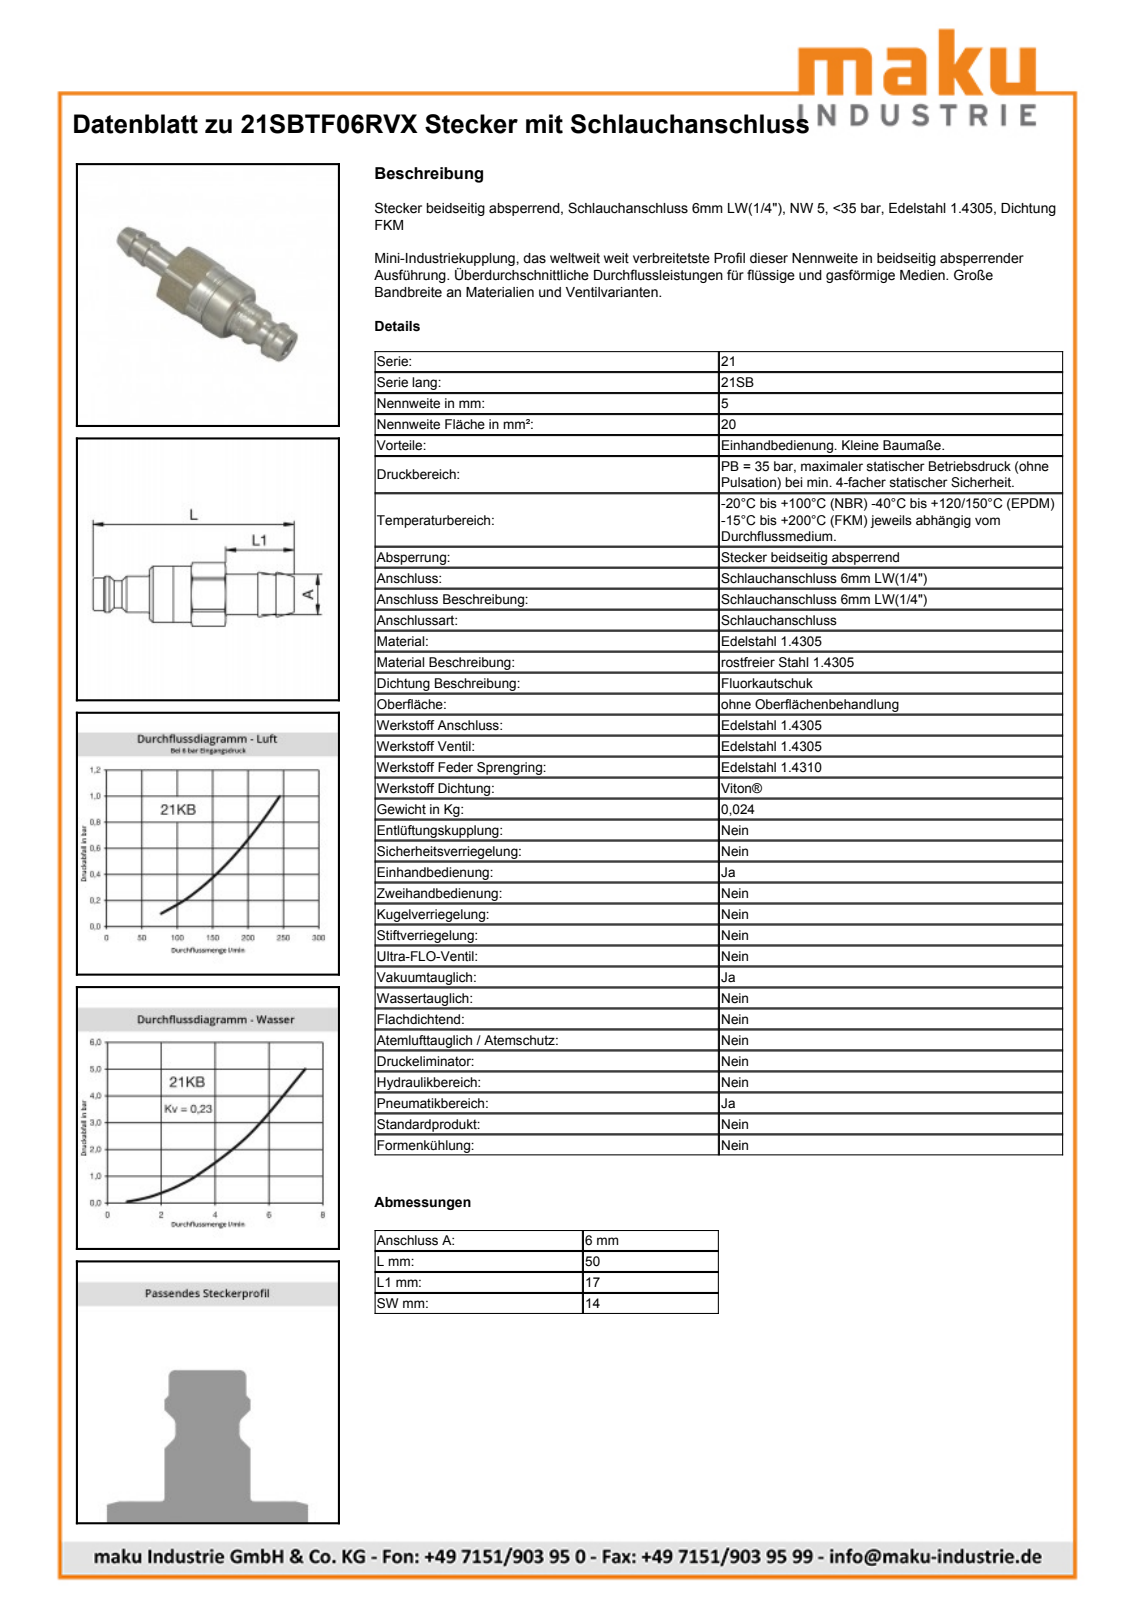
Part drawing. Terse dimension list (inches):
name: D105879
written by: Autodesk Inventor 2013 (AUTOMOTIVE_DESIGN)
unit: in
bodies: 1 solid, 60 faces (15 planar, 16 cylindrical, 29 other)
size: 1.969 × 0.615 × 0.596
volume: 0.26 in³; area: 3.346 in²
holes: 1× ⌀0.472
bosses: 1× ⌀0.551, 1× ⌀0.437, 1× ⌀0.354, 1× ⌀0.319, 1× ⌀0.264, 1× ⌀0.238
rounds: 1× R0.311
face distances: 0.551, 0.744, 0.555, 1.299, 0.984, 0.315, 0.669, 0.429, 1.969, 1.413
